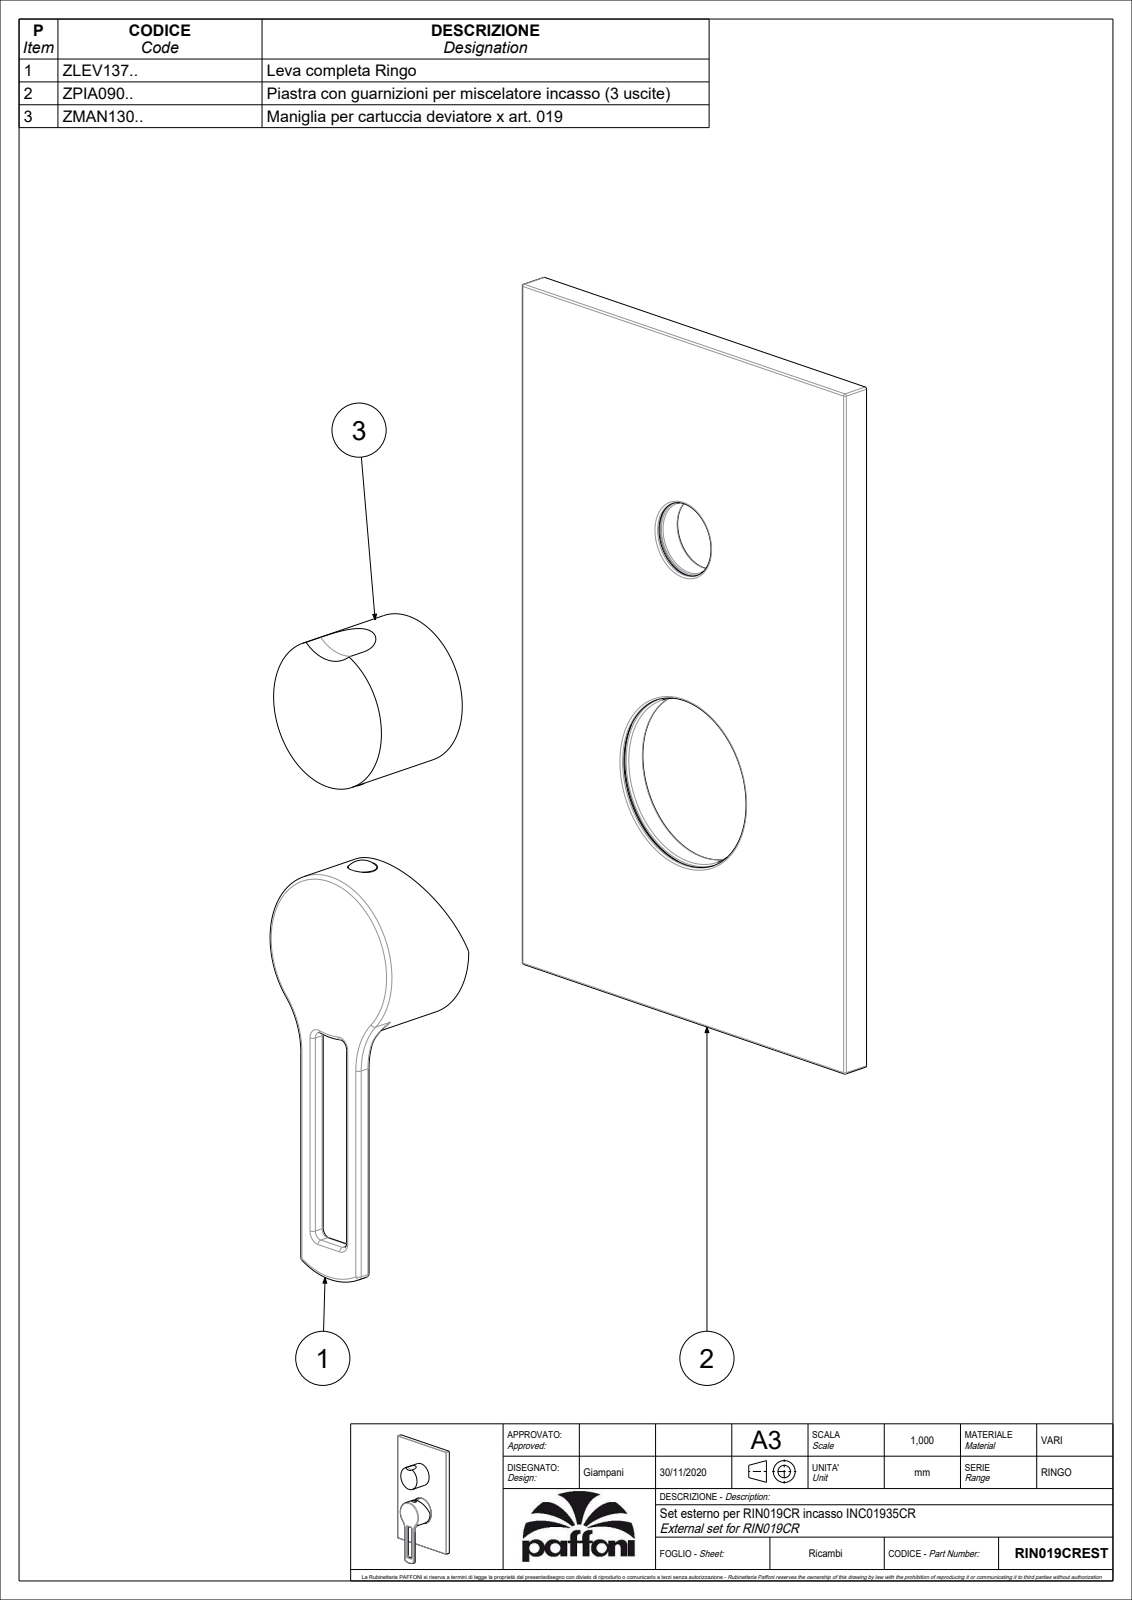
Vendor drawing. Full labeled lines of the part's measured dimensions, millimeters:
Part name (STEP PRODUCT): RIN018CREST
STEP written by: CREO PARAMETRIC BY PTC INC, 2020044 (CONFIG_CONTROL_DESIGN)
Units: millimetres
Bodies: 3 solids, 372 faces (106 planar, 126 cylindrical, 140 other)
Overall size (bounding box): 214 × 120 × 40.35
Volume: 155 078 mm³ · Surface area: 99 558 mm²
Round holes (diameter × count): ⌀3 ×2, ⌀3.2 ×1, ⌀4.2 ×1, ⌀7.8 ×1, ⌀14.8 ×1, ⌀19.2 ×1, ⌀20 ×1, ⌀21 ×1, ⌀23.2 ×1, ⌀36 ×1, ⌀45 ×1, ⌀46 ×1
Round bosses / shafts (diameter × count): ⌀7.6 ×2, ⌀5.5 ×2, ⌀51 ×1, ⌀49 ×1, ⌀44.8 ×1, ⌀40 ×1, ⌀25 ×1, ⌀24 ×1
Partial cylindrical surfaces — rounded edges, fillets, slot ends (radius × count): R1 ×20, R0.5 ×16, R2 ×4, R20 ×2, R12.5 ×1, R21.67 ×1
Main face-to-face distances: 2.5, 8, 5.5, 0.5, 5, 3, 31.5, 22.5, 34.5, 34
Hole centre spacings: 3, 10, 68, 78
